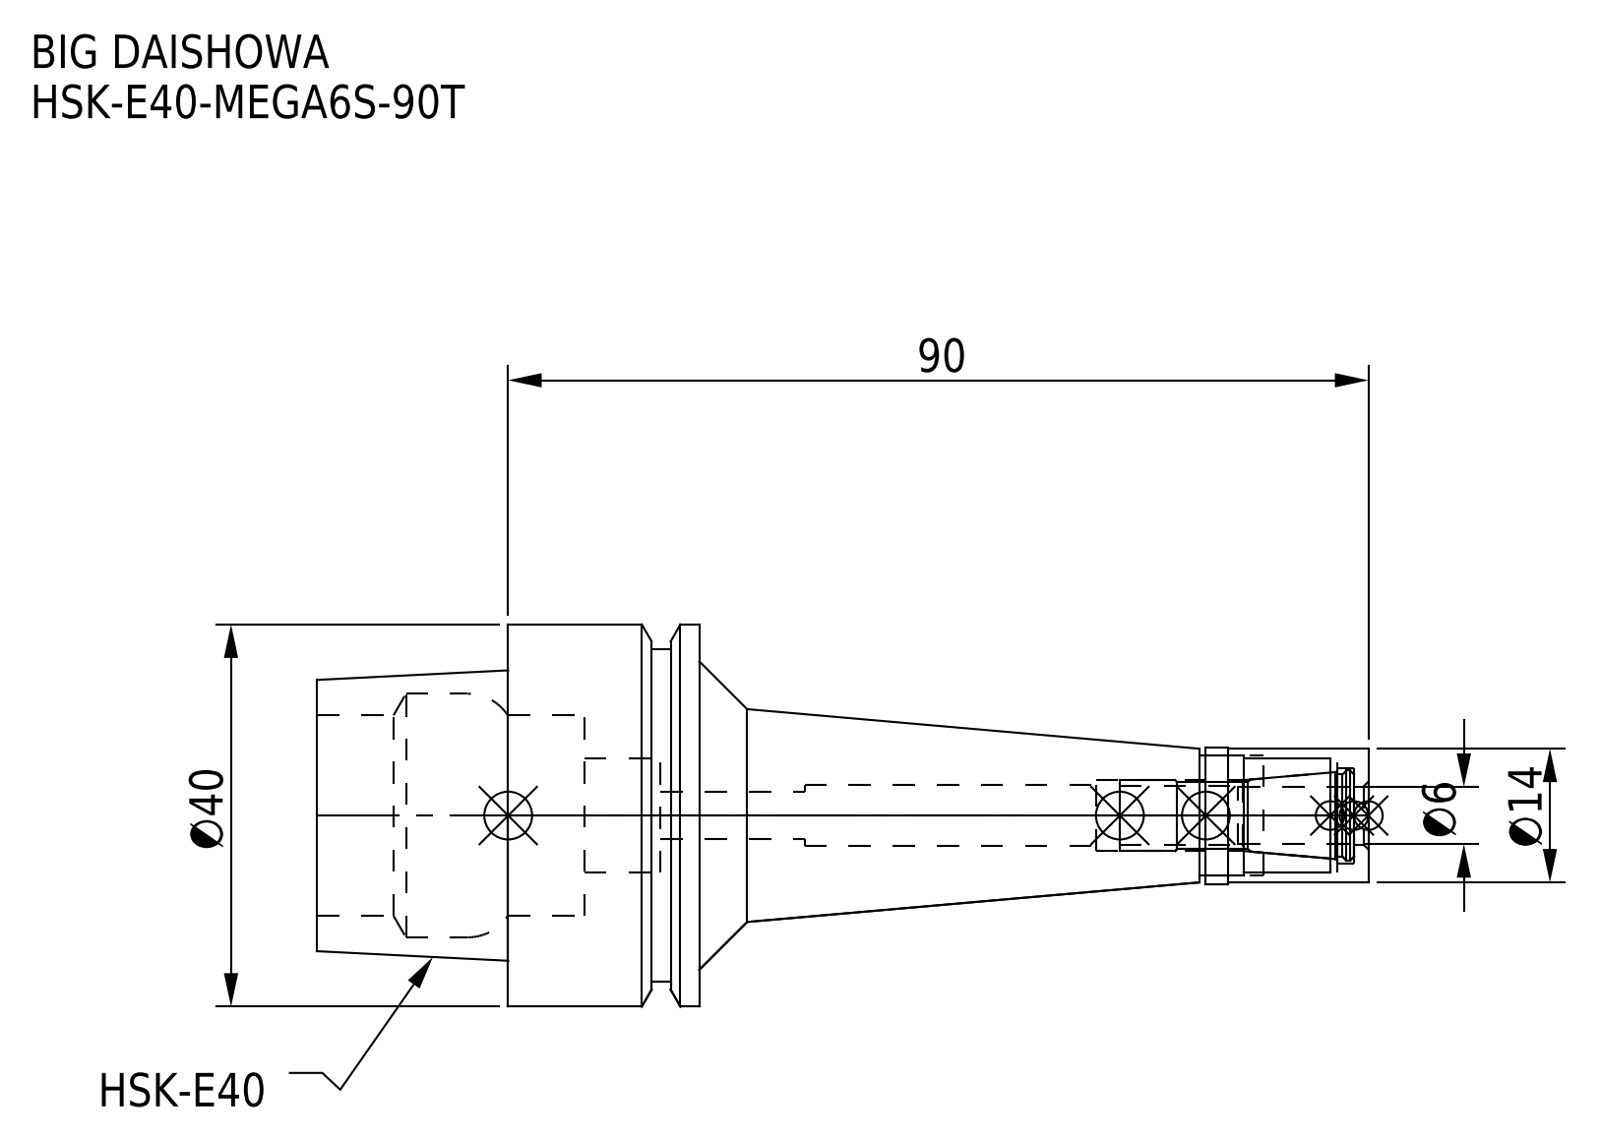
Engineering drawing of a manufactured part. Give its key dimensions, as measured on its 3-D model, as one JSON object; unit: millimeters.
{"part_name": "HSK-E40-MEGA6S-90T; MGN6S_1.stp; HSK-E40-MEGA6S-90T-060.stp; HSK-E40-MEGA6S-90T-060-FreeParts (+3 more)", "step_written_by": "SolidWorks 2019 (CONFIG_CONTROL_DESIGN)", "units": "millimeters", "bodies": {"solids": 2, "faces": 74, "planar": 18, "cylindrical": 38, "other": 18}, "overall_size": [110, 40, 40], "volume_mm3": 41056, "surface_area_mm2": 15782, "round_holes": [[5, 1], [6.1, 1], [6.4, 1], [7.4, 1], [10, 1], [12, 1], [12.5, 1], [21, 1], [25.5, 1]], "round_bosses_or_shafts": [[40, 1], [34.8, 1], [14.3, 1], [14, 1]], "face_to_face_distances": [20, 40, 12.05, 7.95, 27.95, 17, 73, 70, 82.05, 90]}
